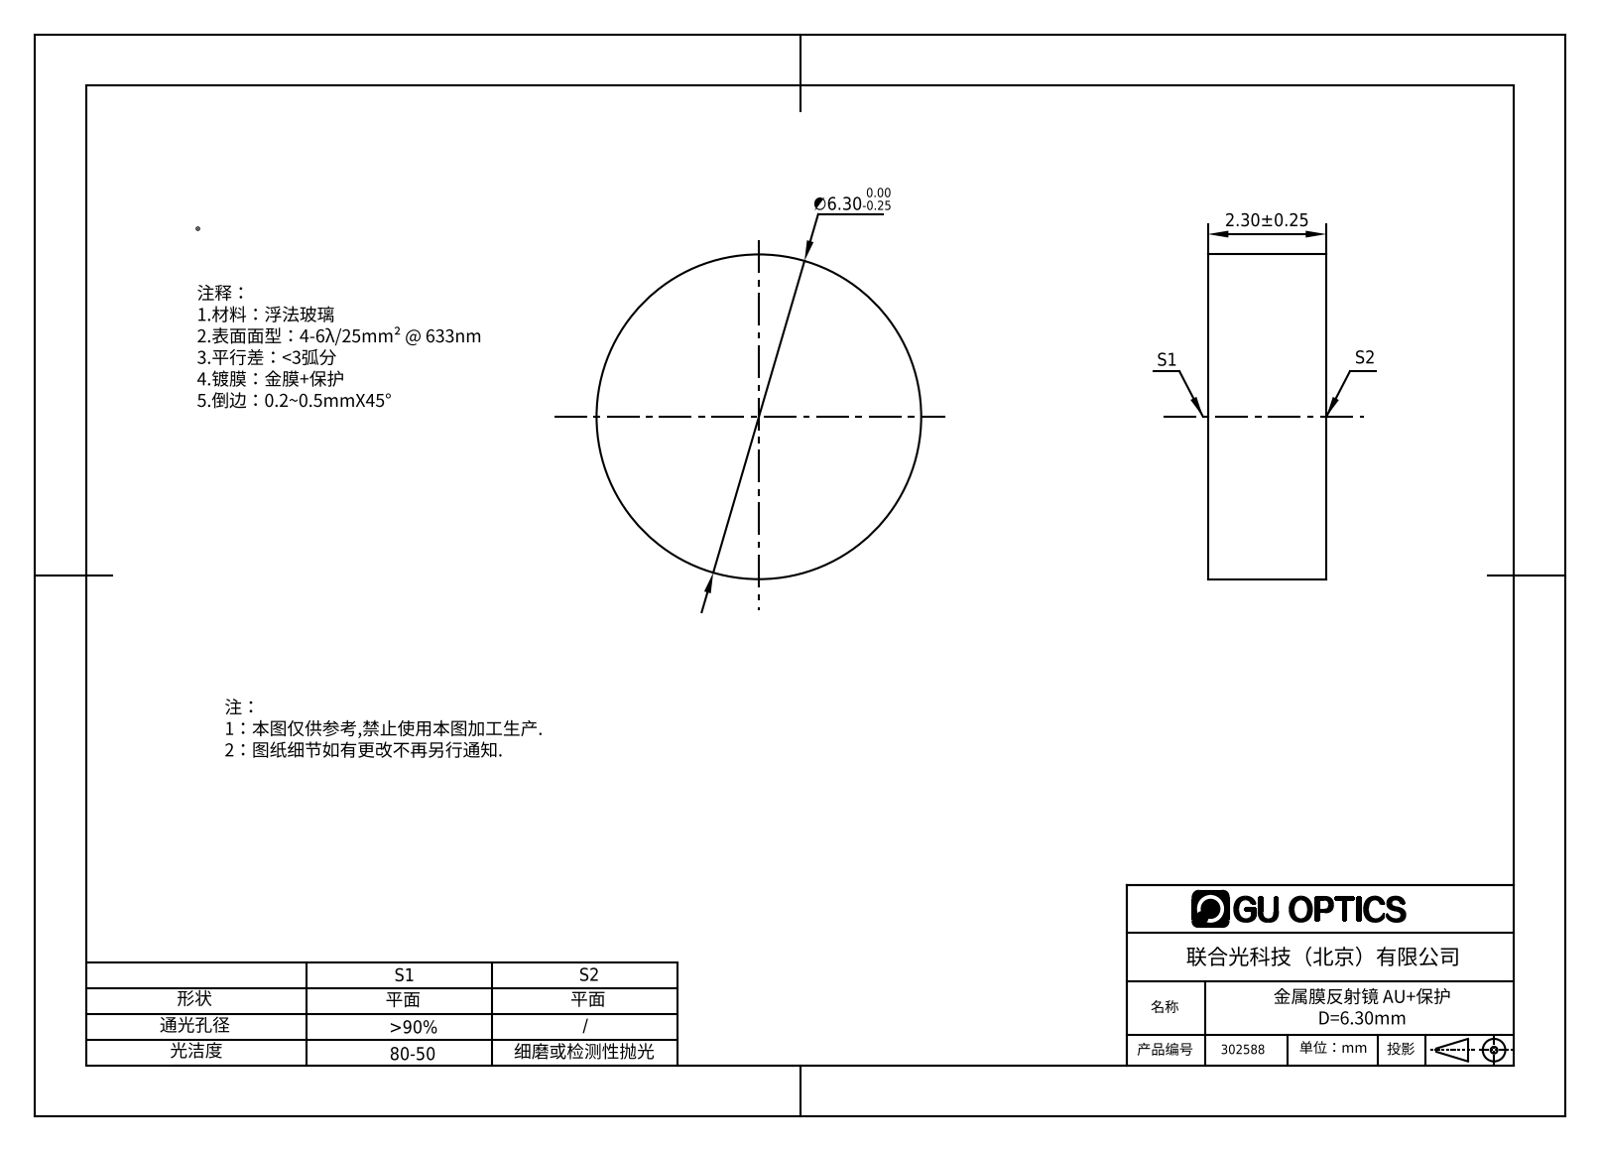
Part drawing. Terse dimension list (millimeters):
name: 302501
written by: SolidWorks 2016 (AUTOMOTIVE_DESIGN)
unit: mm
bodies: 1 solid, 4 faces (2 planar, 2 cylindrical, 0 other)
size: 6.3 × 6.3 × 2.3
volume: 72 mm³; area: 108 mm²
bosses: 1× ⌀6.3
face distances: 2.3
